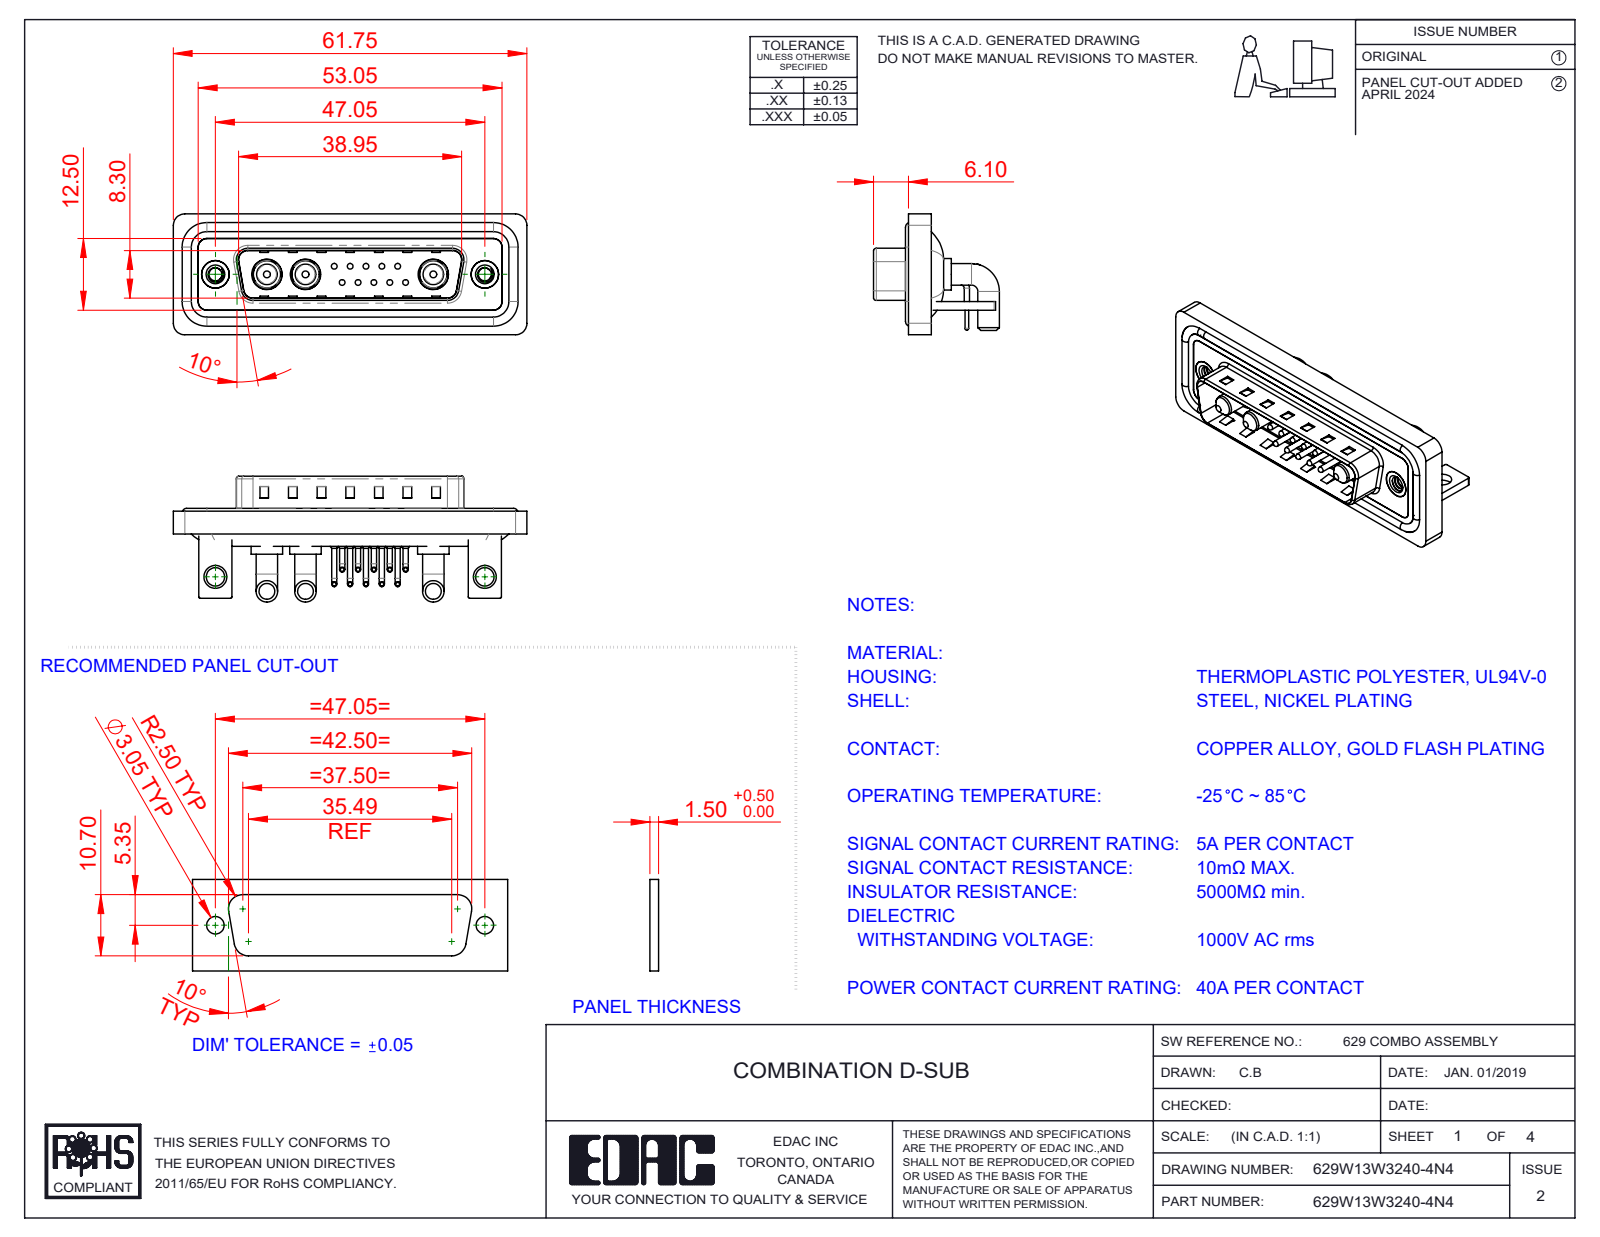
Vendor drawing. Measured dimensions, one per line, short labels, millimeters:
name: 629Combo Contact Row 1; 629Combo Stabilizer Bracket; 629Combo Housing_13W3; 629Combo Contact Row 2 (+6 more)
written by: SolidWorks 2023 (CONFIG_CONTROL_DESIGN)
unit: mm
bodies: 25 solids, 1752 faces (899 planar, 629 cylindrical, 224 other)
size: 61.75 × 21.98 × 21.1
volume: 8 106 mm³; area: 13 215 mm²
holes: 10× ⌀0.75, 10× ⌀1.6, 10× ⌀2, 3× ⌀4.85, 3× ⌀5.3, 2× ⌀2.26, 2× ⌀3.2, 2× ⌀4, 2× ⌀4.8, 2× ⌀5
bosses: 20× ⌀0.9, 10× ⌀1.5, 10× ⌀1, 10× ⌀0.65, 6× ⌀3.75, 4× ⌀1.6, 3× ⌀5.5, 3× ⌀5.2
rounds: 19× R2, 18× R1.5, 16× R0.25, 10× R1.01, 9× R0.5, 8× R1.6, 4× R0.6, 4× R0.65
face distances: 0.4, 0.8, 1.5, 2.9, 2.1, 1.1, 4.1, 1.6, 3.7, 4.5
hole spacings: 3.16, 2.77, 5.04, 5.54, 7.49, 5.03, 8.31, 10.11
